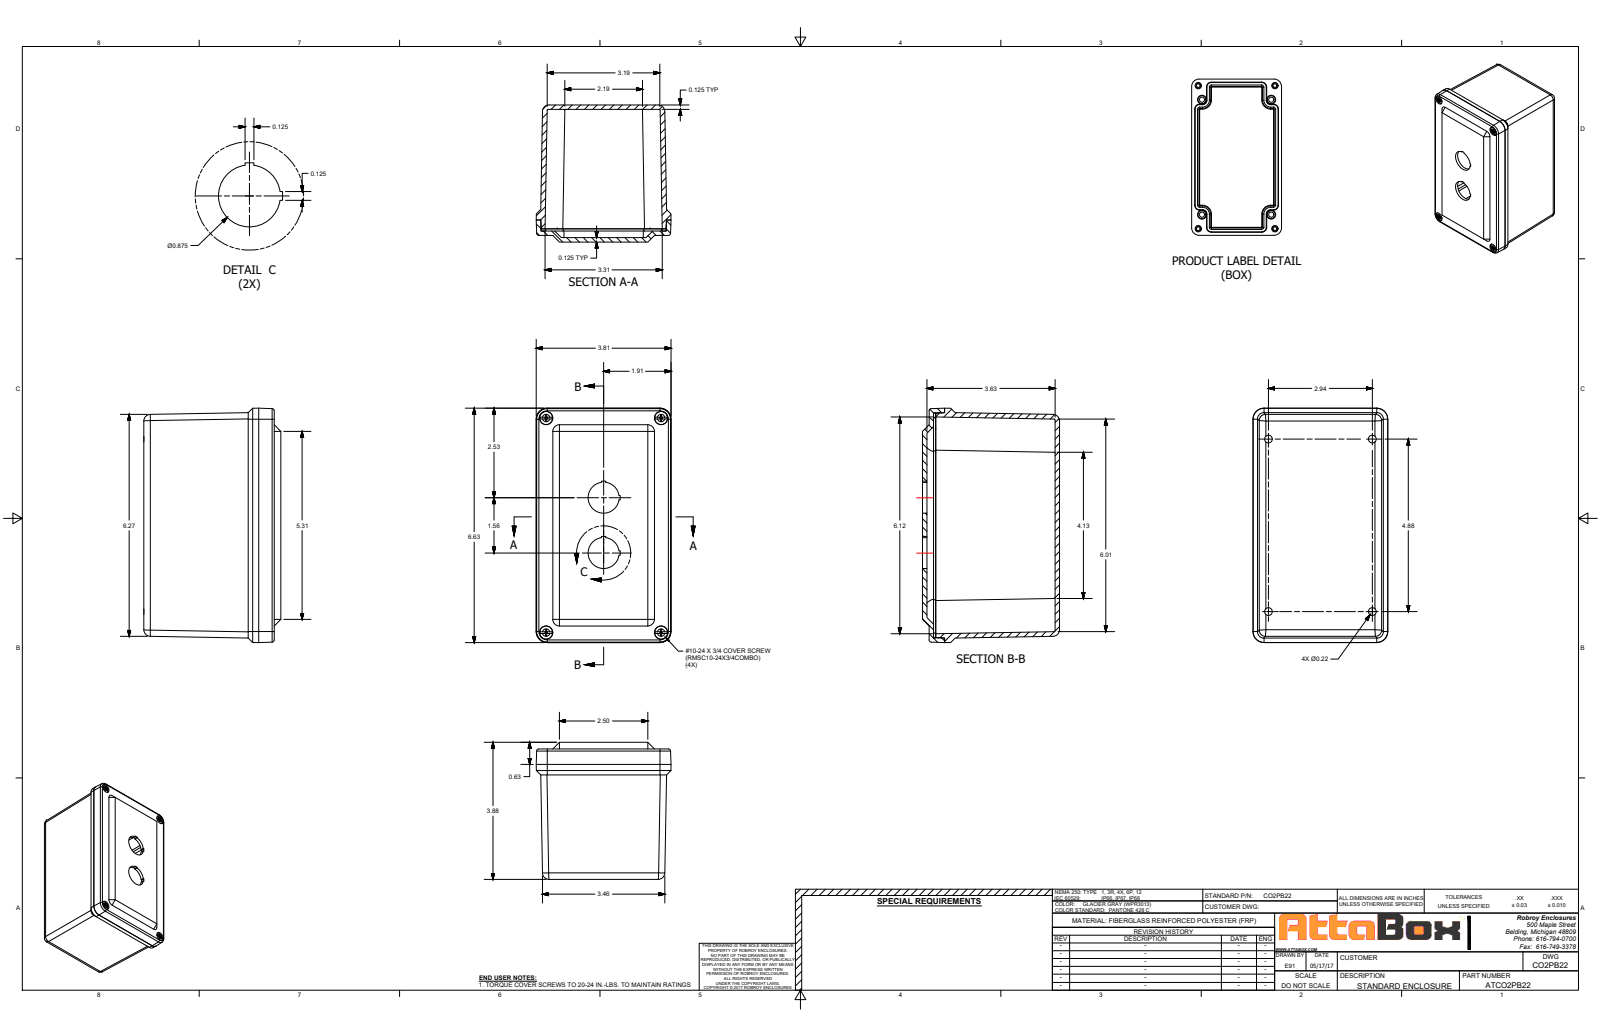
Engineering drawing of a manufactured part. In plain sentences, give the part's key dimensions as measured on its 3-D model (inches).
The part is named "CO2PB22". Its 3-D file was written by "SolidWorks 2018 (AUTOMOTIVE_DESIGN)". It is 11 solids with 395 faces: 195 planar, 104 cylindrical and 96 other. Overall it measures 6.625 by 3.875 by 3.812 inches. Its volume is 20.2 cubic inches and its surface area 266 square inches. Round holes: 8 of diameter 0.219, 4 of diameter 0.159, 4 of diameter 0.19, 4 of diameter 0.375, 2 of diameter 0.875. Round bosses or shafts: 4 of diameter 0.371, 4 of diameter 0.27, 4 of diameter 0.177. Partial cylindrical surfaces (rounded edges, fillets, slot ends): 20 of radius 0.031, 16 of radius 0.012, 4 of radius 0.176, 4 of radius 0.22, 4 of radius 0.313, 4 of radius 0.325, 2 of radius 0.062, 2 of radius 0.063. The main face-to-face distances are 0.125, 0.131, 3.75, 0.187, 3.563, 0.5, 3.875, 3.625, 0.063, 3.438. The hole center spacings are 0.614, 2.214, 2.775, 3.15, 3.538, 4.144, 5.471, 6.283.
